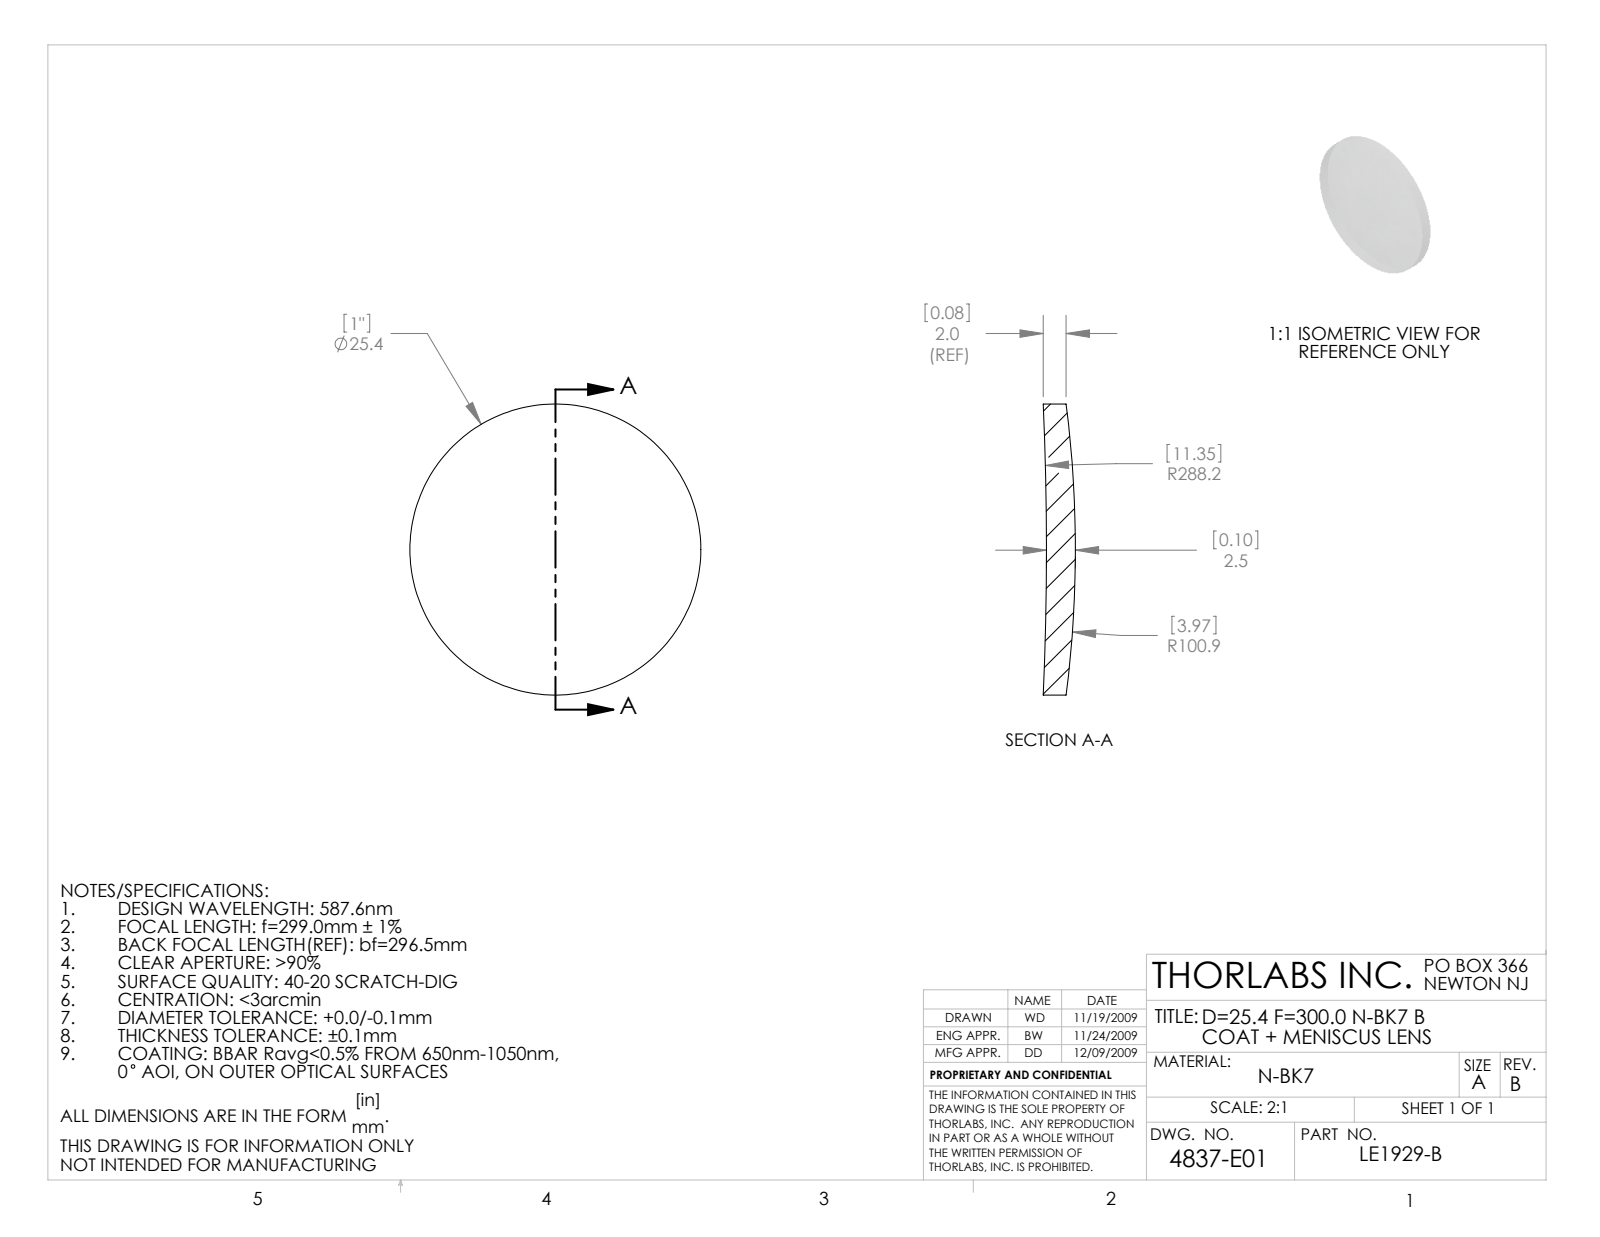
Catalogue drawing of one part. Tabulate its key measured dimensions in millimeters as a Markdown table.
| quantity | value |
| --- | --- |
| part name | 4837-E0W |
| STEP written by | SolidWorks 2009 (AUTOMOTIVE_DESIGN) |
| units | millimeters |
| bodies | 1 solid, 6 faces (0 planar, 2 cylindrical, 4 other) |
| overall size | 25.4 × 25.4 × 2.8 |
| volume | 1 145 mm³ |
| surface area | 1 175 mm² |
| round bosses / shafts (diameter × count) | 25.4 × 1 |
